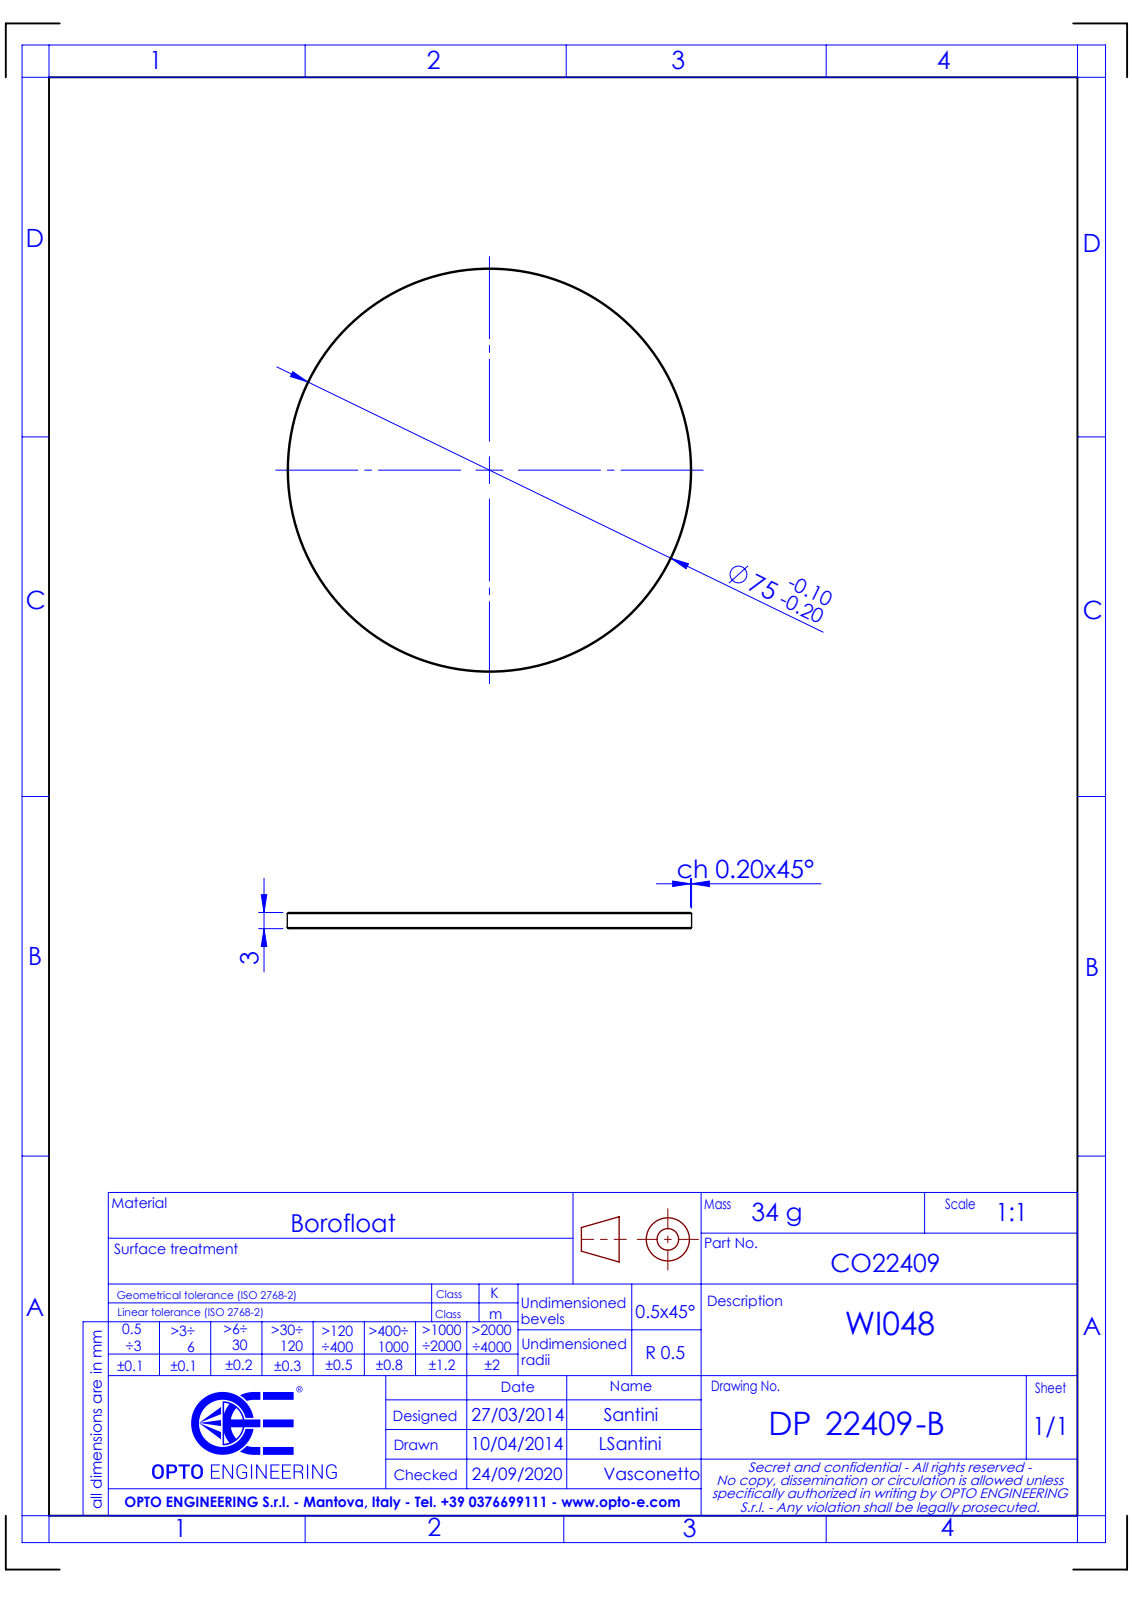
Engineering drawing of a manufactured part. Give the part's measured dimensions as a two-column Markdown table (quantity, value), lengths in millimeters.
| quantity | value |
| --- | --- |
| part name | DP22409_WI048 |
| STEP written by | SolidWorks 2021 (CONFIG_CONTROL_DESIGN) |
| units | millimeters |
| bodies | 1 solid, 8 faces (2 planar, 2 cylindrical, 4 other) |
| overall size | 75 × 75 × 3 |
| volume | 13 244 mm³ |
| surface area | 9 487 mm² |
| round bosses / shafts (diameter × count) | 75 × 1 |
| main face-to-face distances | 3 |
